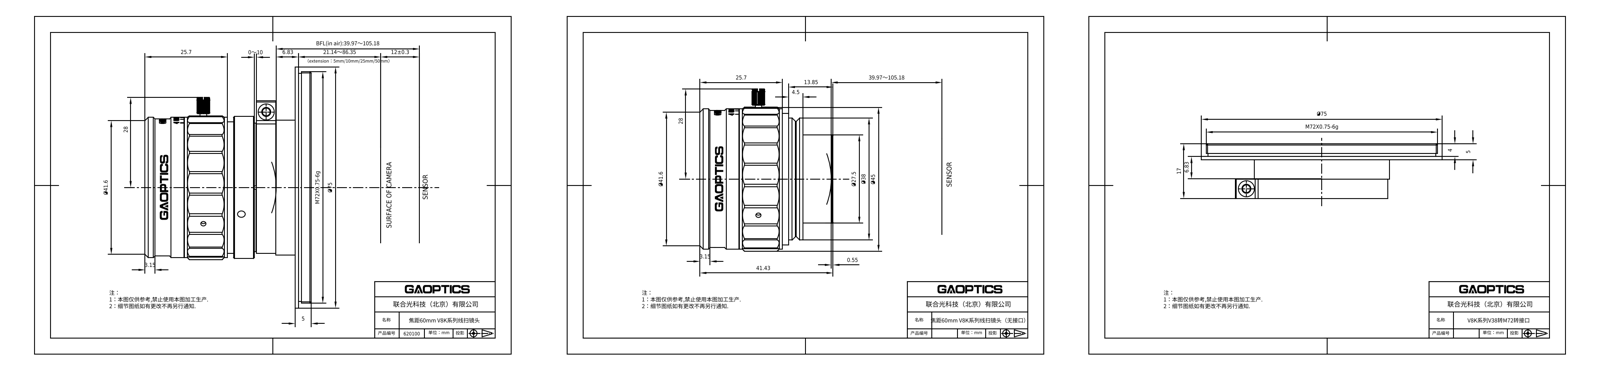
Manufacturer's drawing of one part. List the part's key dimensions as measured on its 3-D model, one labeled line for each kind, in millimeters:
Part name (STEP PRODUCT): 620100; 接口配件2; 接口配件3; 620100带接口 (+1 more)
STEP written by: SolidWorks 2019 (CONFIG_CONTROL_DESIGN)
Units: millimetres
Bodies: 8 solids, 1491 faces (501 planar, 264 cylindrical, 726 other)
Overall size (bounding box): 75 × 75 × 51.78
Volume: 54 506 mm³ · Surface area: 38 093 mm²
Round holes (diameter × count): ⌀1.6 ×3, ⌀2.6 ×3, ⌀2.4 ×1, ⌀3.2 ×1, ⌀5 ×1, ⌀18.63 ×1, ⌀19.02 ×1, ⌀19.4 ×1, ⌀19.8 ×1, ⌀20.2 ×1, ⌀20.6 ×1, ⌀21 ×1
Round bosses / shafts (diameter × count): ⌀75 ×1, ⌀72 ×1, ⌀71 ×1, ⌀44.2 ×1, ⌀43.6 ×1, ⌀42.6 ×1, ⌀42 ×1, ⌀41 ×1
Partial cylindrical surfaces — rounded edges, fillets, slot ends (radius × count): R1 ×23, R12 ×21, R2 ×1, R12.05 ×1, R21.25 ×1, R21.75 ×1, R27 ×1
Main face-to-face distances: 1, 5, 4, 19.2, 2, 43.78, 7, 6, 14.7, 15.7
